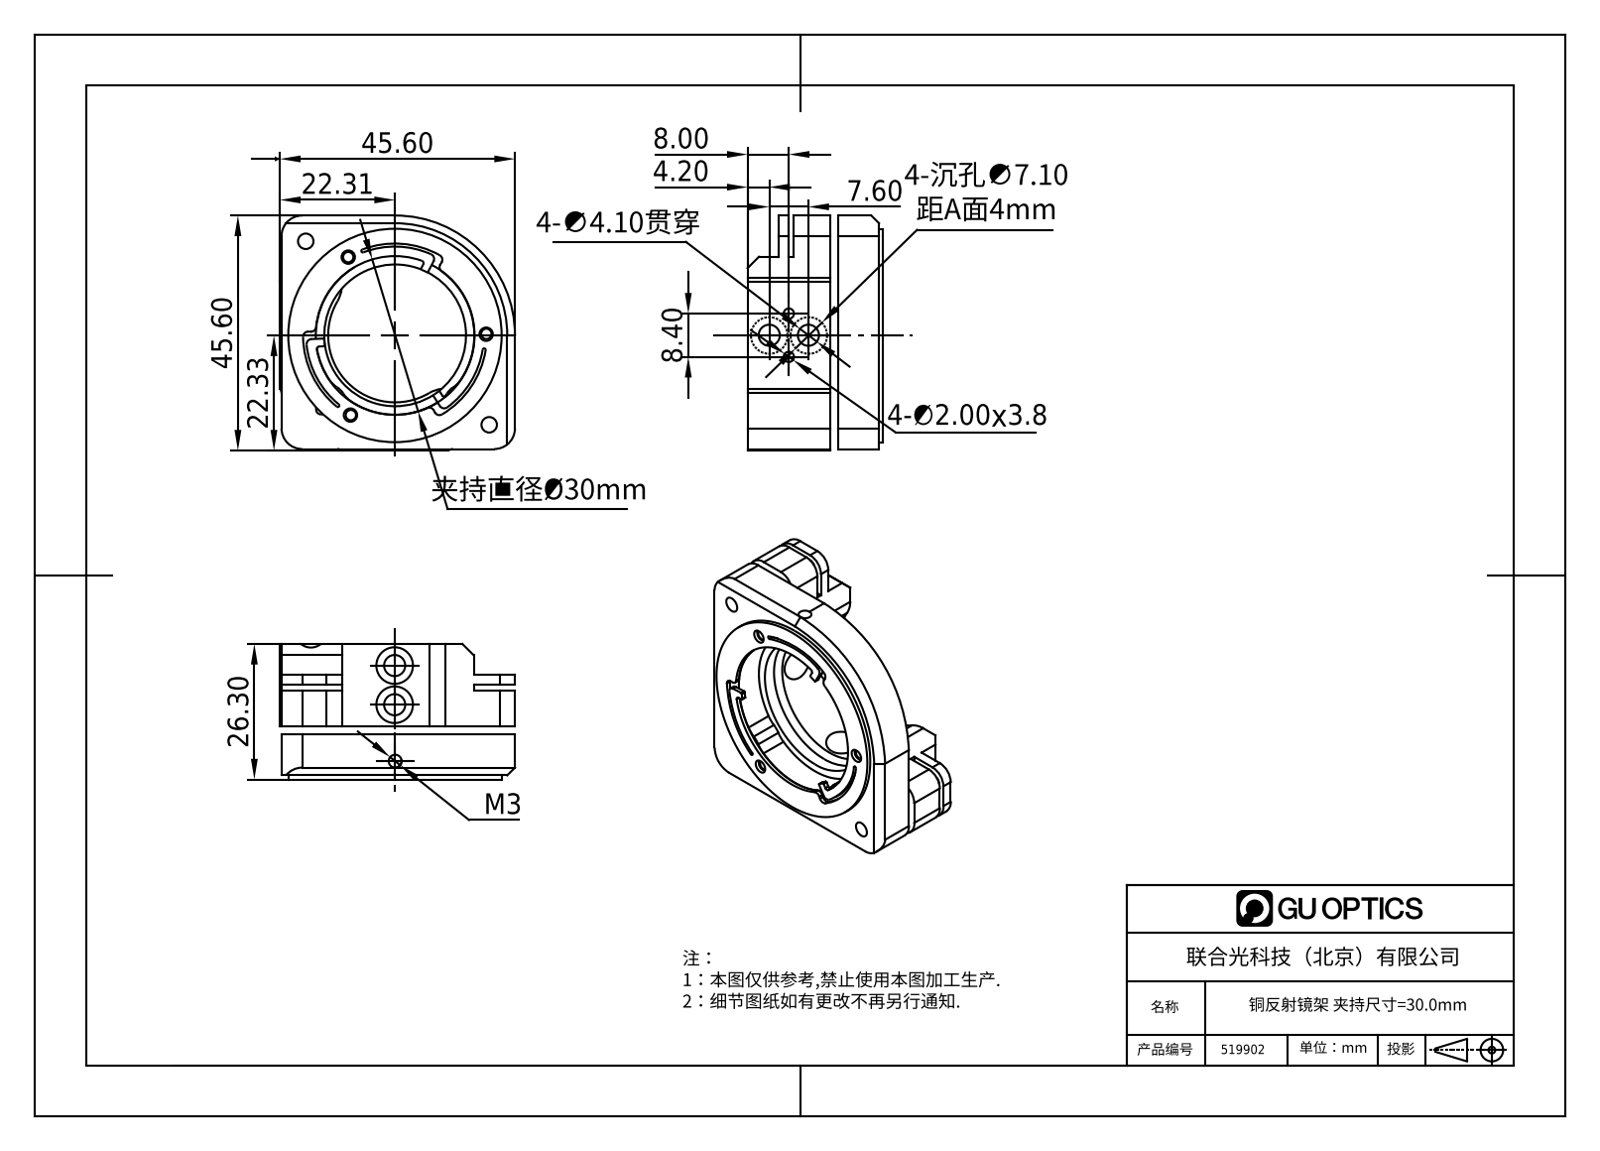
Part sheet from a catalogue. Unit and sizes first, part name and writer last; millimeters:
Units: millimetres
Overall size (bounding box): 45.6 × 45.6 × 26.3
Round holes (diameter × count): ⌀2 ×10, ⌀4.1 ×4, ⌀7.1 ×4, ⌀2.5 ×3, ⌀2.6 ×3, ⌀3.5 ×3, ⌀6 ×3, ⌀3 ×2, ⌀4.5 ×2, ⌀5 ×2, ⌀30.8 ×2, ⌀27.5 ×1
Round bosses / shafts (diameter × count): ⌀41.4 ×1
Partial cylindrical surfaces — rounded edges, fillets, slot ends (radius × count): R1 ×9, R0.2 ×6, R4 ×5, R1.55 ×4, R5 ×4, R0.29 ×3, R0.5 ×3, R3 ×2
Main face-to-face distances: 8, 9.5, 1.5, 17.5, 16, 25.5, 0.8, 8.8, 10.3, 26.3
Hole centre spacings: 5.66, 17.7, 25.18, 30.65, 19.57, 4.77, 7.57, 7.6
Volume: 19 642 mm³ · Surface area: 12 871 mm²
Bodies: 3 solids, 221 faces (61 planar, 151 cylindrical, 9 other)
Part name (STEP PRODUCT): 二维镜架30.0完整
STEP written by: SolidWorks 2016 (AUTOMOTIVE_DESIGN)
